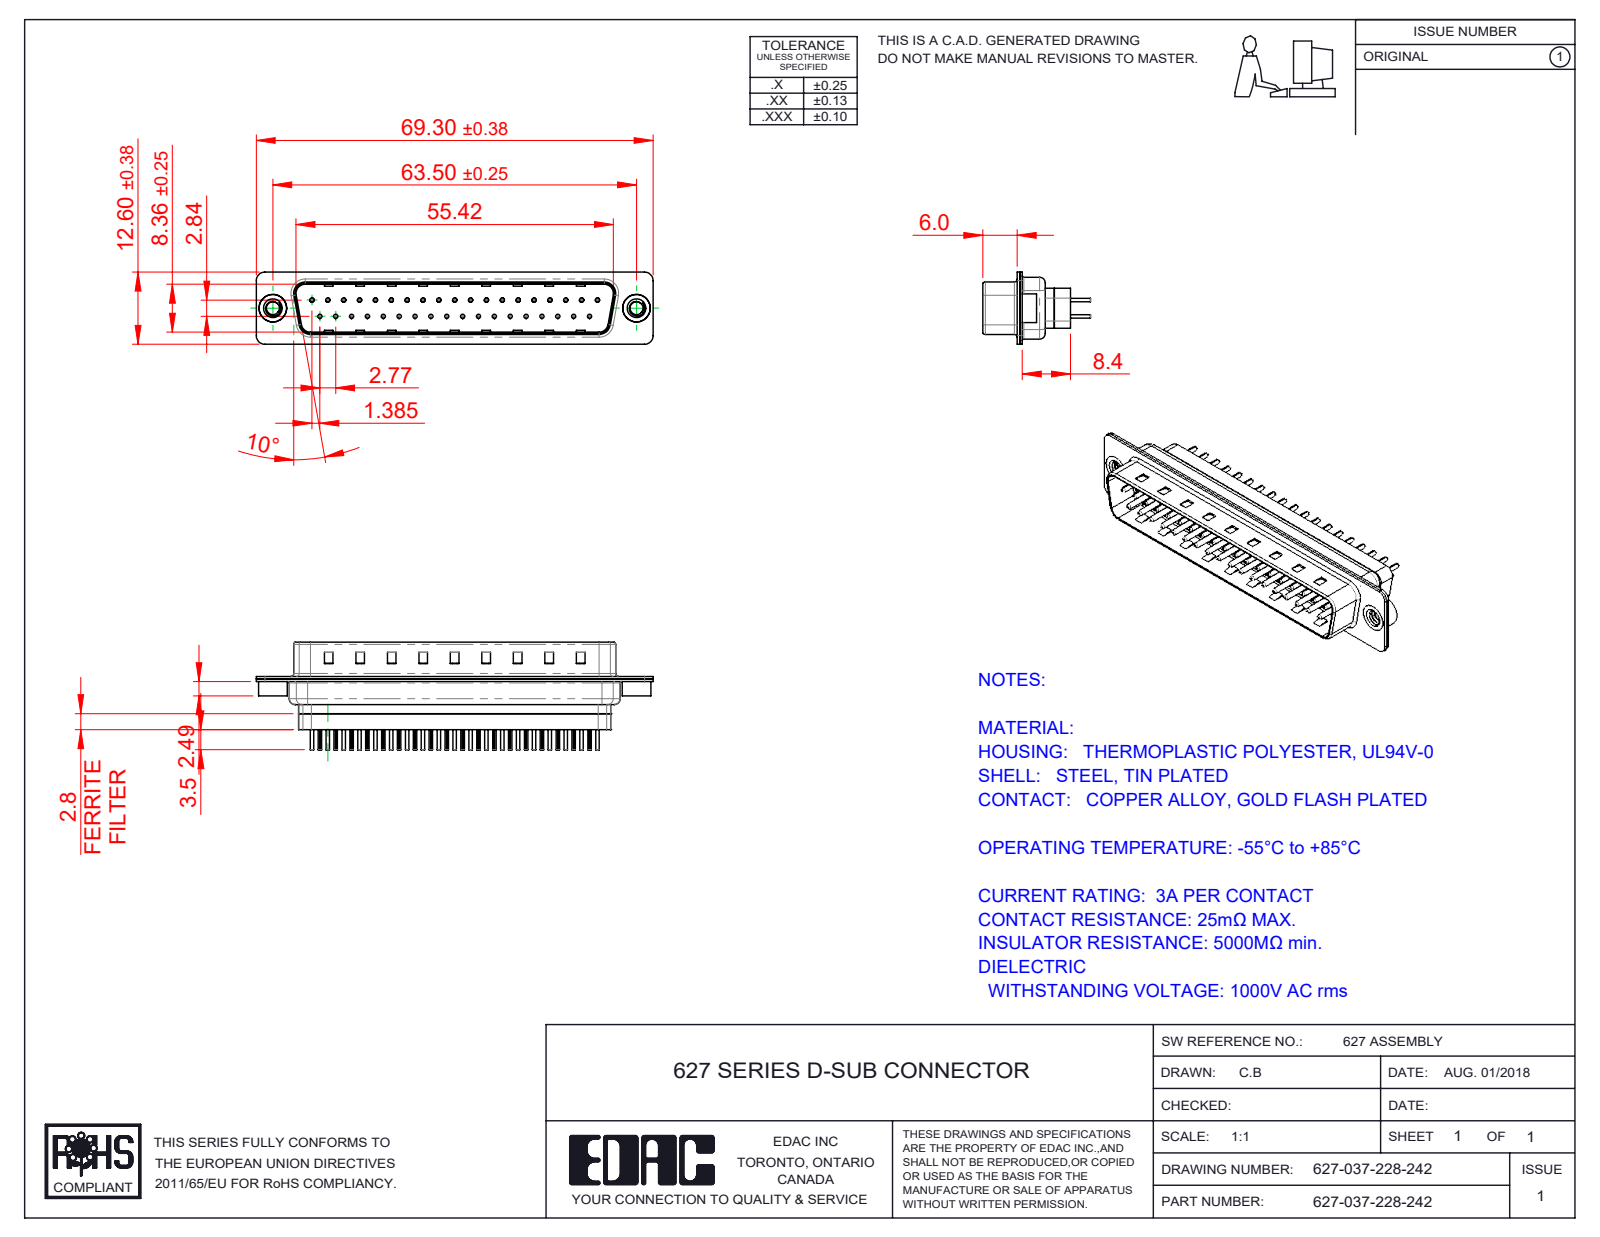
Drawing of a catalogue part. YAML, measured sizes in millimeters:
part_name: "627-037-228-042; 627 Shell Rear_37 Contacts; 627 Contact Row 2_28L; 627 4-40 Threaded Rivet (+3 more)"
step_written_by: "SolidWorks 2020 (CONFIG_CONTROL_DESIGN)"
units: millimeters
bodies: {solids: 43, faces: 4119, planar: 1097, cylindrical: 1587, other: 1435}
overall_size: [69.3, 18.8, 12.6]
volume: 4551
surface_area: 12285
round_holes:
  - {diameter: 0.2, count: 37}
  - {diameter: 0.35, count: 37}
  - {diameter: 1.1, count: 37}
  - {diameter: 1.6, count: 37}
  - {diameter: 2.26, count: 2}
  - {diameter: 4, count: 2}
  - {diameter: 4.8, count: 2}
round_bosses_or_shafts:
  - {diameter: 2, count: 37}
  - {diameter: 1.5, count: 37}
  - {diameter: 0.75, count: 37}
  - {diameter: 0.6, count: 37}
  - {diameter: 5, count: 2}
  - {diameter: 4.9, count: 2}
partial_cylinders:
  - {radius: 0.1, count: 74}
  - {radius: 1.5, count: 16}
  - {radius: 2, count: 12}
  - {radius: 0.5, count: 8}
  - {radius: 1.6, count: 8}
  - {radius: 0.25, count: 4}
  - {radius: 0.6, count: 4}
  - {radius: 0.65, count: 4}
face_to_face_distances: [0.4, 6.05, 0.82, 9.58, 0.45, 8.4, 0.68, 7.68, 1.5, 1.08]
hole_center_spacings: [3.16, 2.77, 5.54, 8.31, 5.04, 10.1, 11.08, 12.78]
